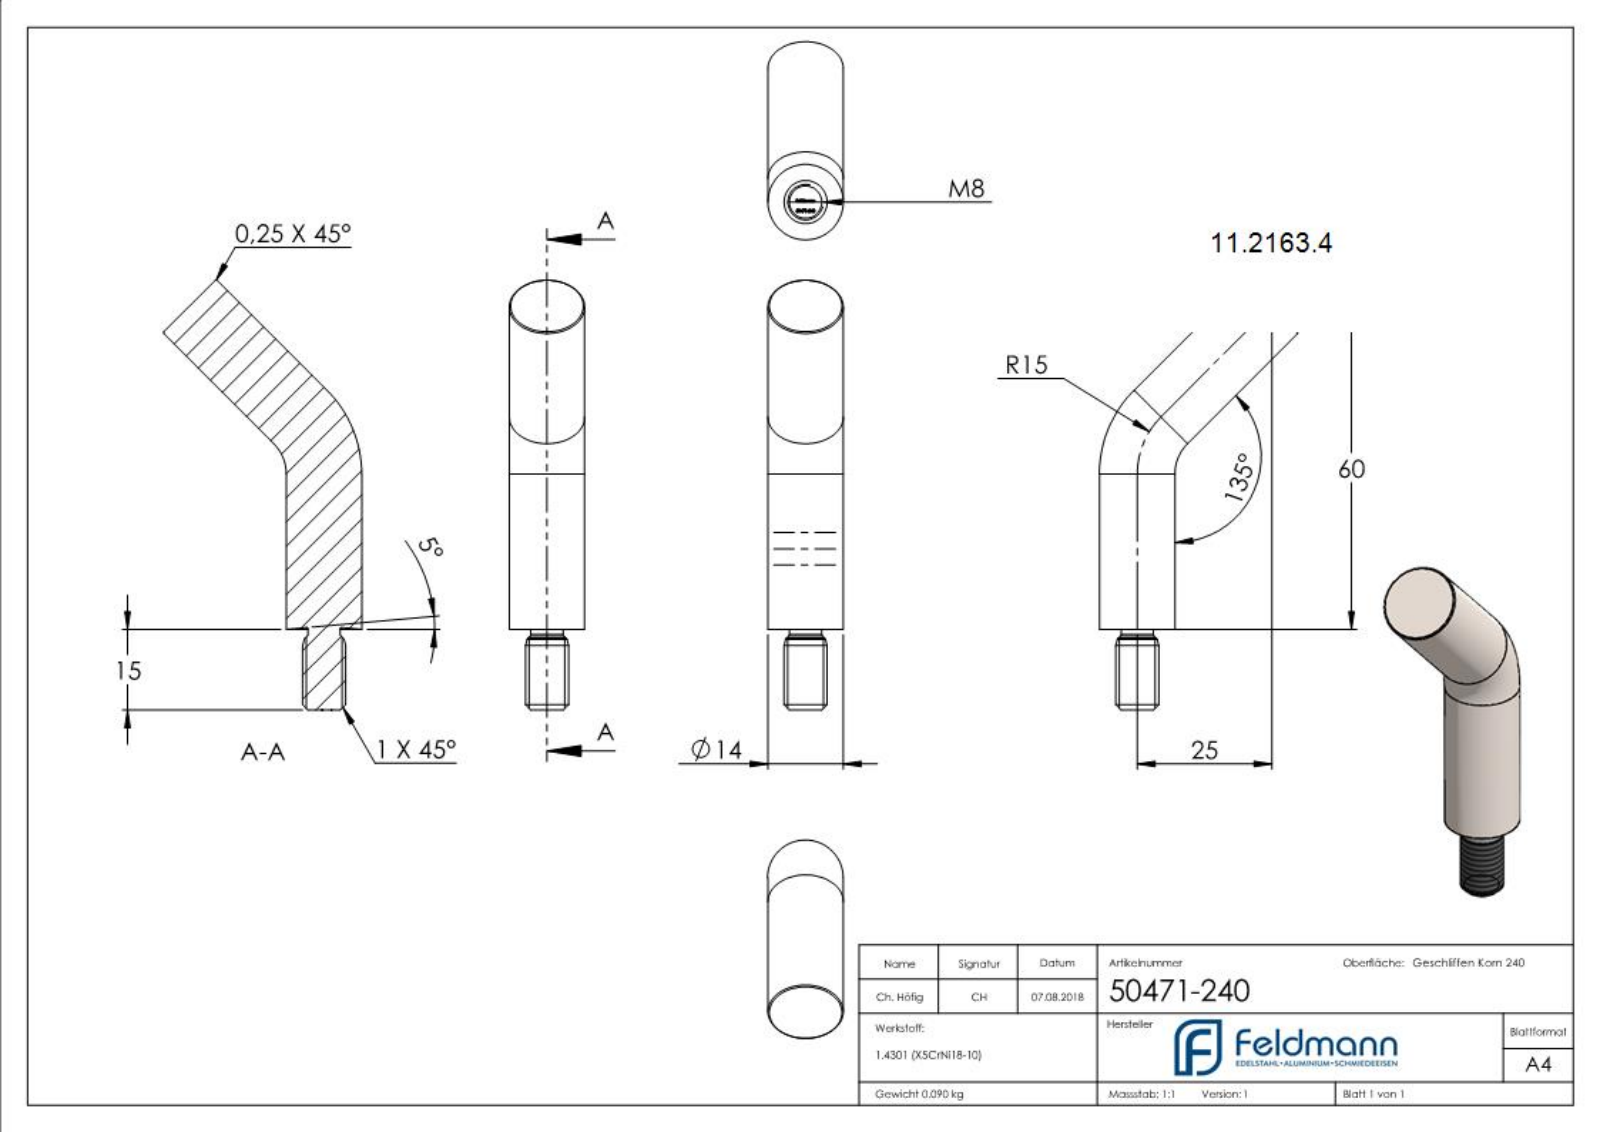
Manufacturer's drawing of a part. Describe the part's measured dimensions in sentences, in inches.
The part is named "50471-240". Its 3-D file was written by "SolidWorks 2015 (CONFIG_CONTROL_DESIGN)". It is 1 solid with 242 faces: 134 planar, 8 cylindrical and 100 other. Overall it measures 3.141 by 1.448 by 0.551 inches. Its volume is 0.697 cubic inches and its surface area 5.819 square inches. Round bosses or shafts: 2 of diameter 0.551, 1 of diameter 0.315, 1 of diameter 0.236. The main face-to-face distances are 0.074, 0.053, 0.019, 0.047, 0.014, 0.038, 0.072, 0.045, 0.083, 0.017.
